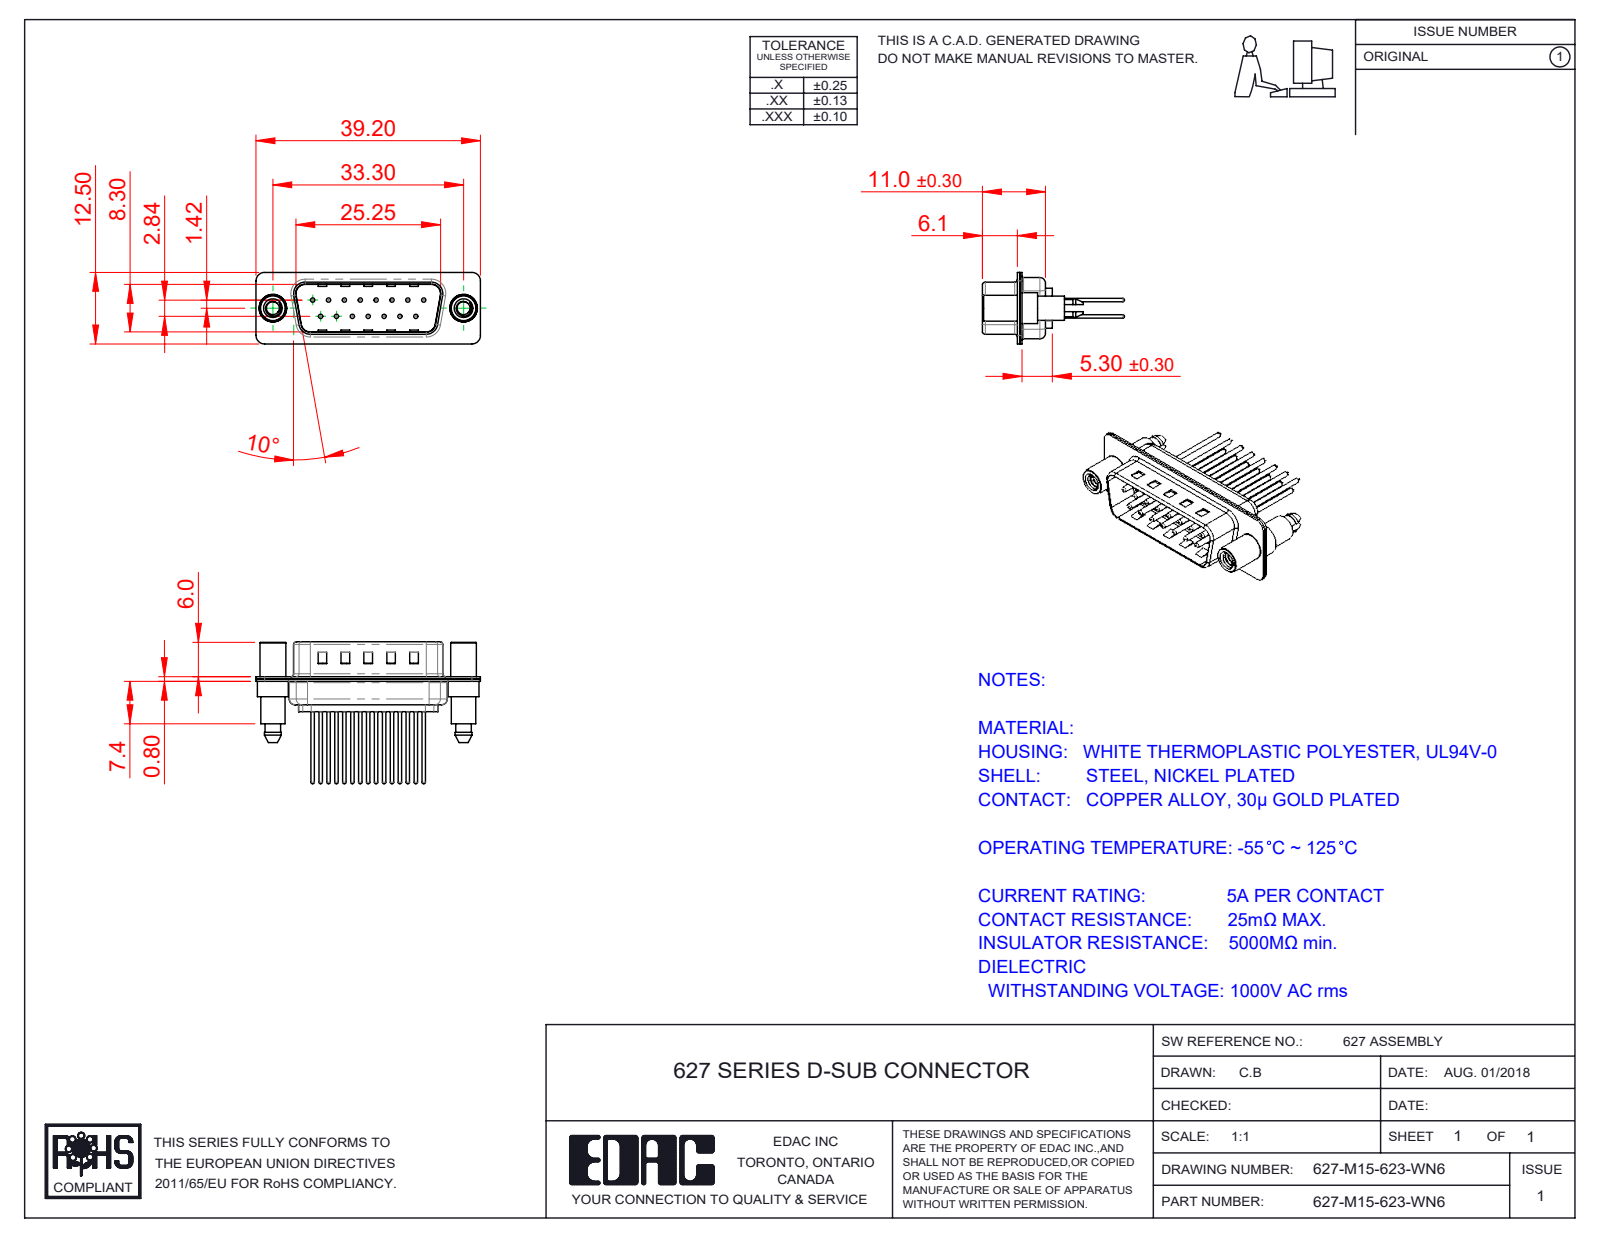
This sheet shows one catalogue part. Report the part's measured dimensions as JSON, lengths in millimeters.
{"part_name": "627M Housing_15 Contacts; 627M Contact Row 2_23; 627M Shell Front_15 Contacts; 627M Shell Rear_15 Contacts (+3 more)", "step_written_by": "SolidWorks 2020 (CONFIG_CONTROL_DESIGN)", "units": "millimeters", "bodies": {"solids": 20, "faces": 947, "planar": 262, "cylindrical": 371, "other": 314}, "overall_size": [39.2, 24.77, 12.5], "volume_mm3": 2211, "surface_area_mm2": 5471, "round_holes": [[0.75, 15], [1.6, 15], [2, 15], [2.26, 2], [4, 2], [4.8, 2]], "round_bosses_or_shafts": [[1.5, 15], [0.6, 15], [5.4, 2], [4.9, 2], [4.5, 2], [4.25, 2]], "partial_cylinders_radius": [[1.5, 18], [2, 12], [1.6, 10], [0.5, 8], [0.25, 4], [0.6, 4], [0.65, 4], [0.9, 4]], "face_to_face_distances": [0.4, 0.8, 9.5, 9.1, 8.7, 9.9, 5.3, 1.2, 6.1, 5.7], "hole_center_spacings": [3.16, 2.77, 5.54, 8.31, 11.08, 5.03, 5.04, 7.48]}
